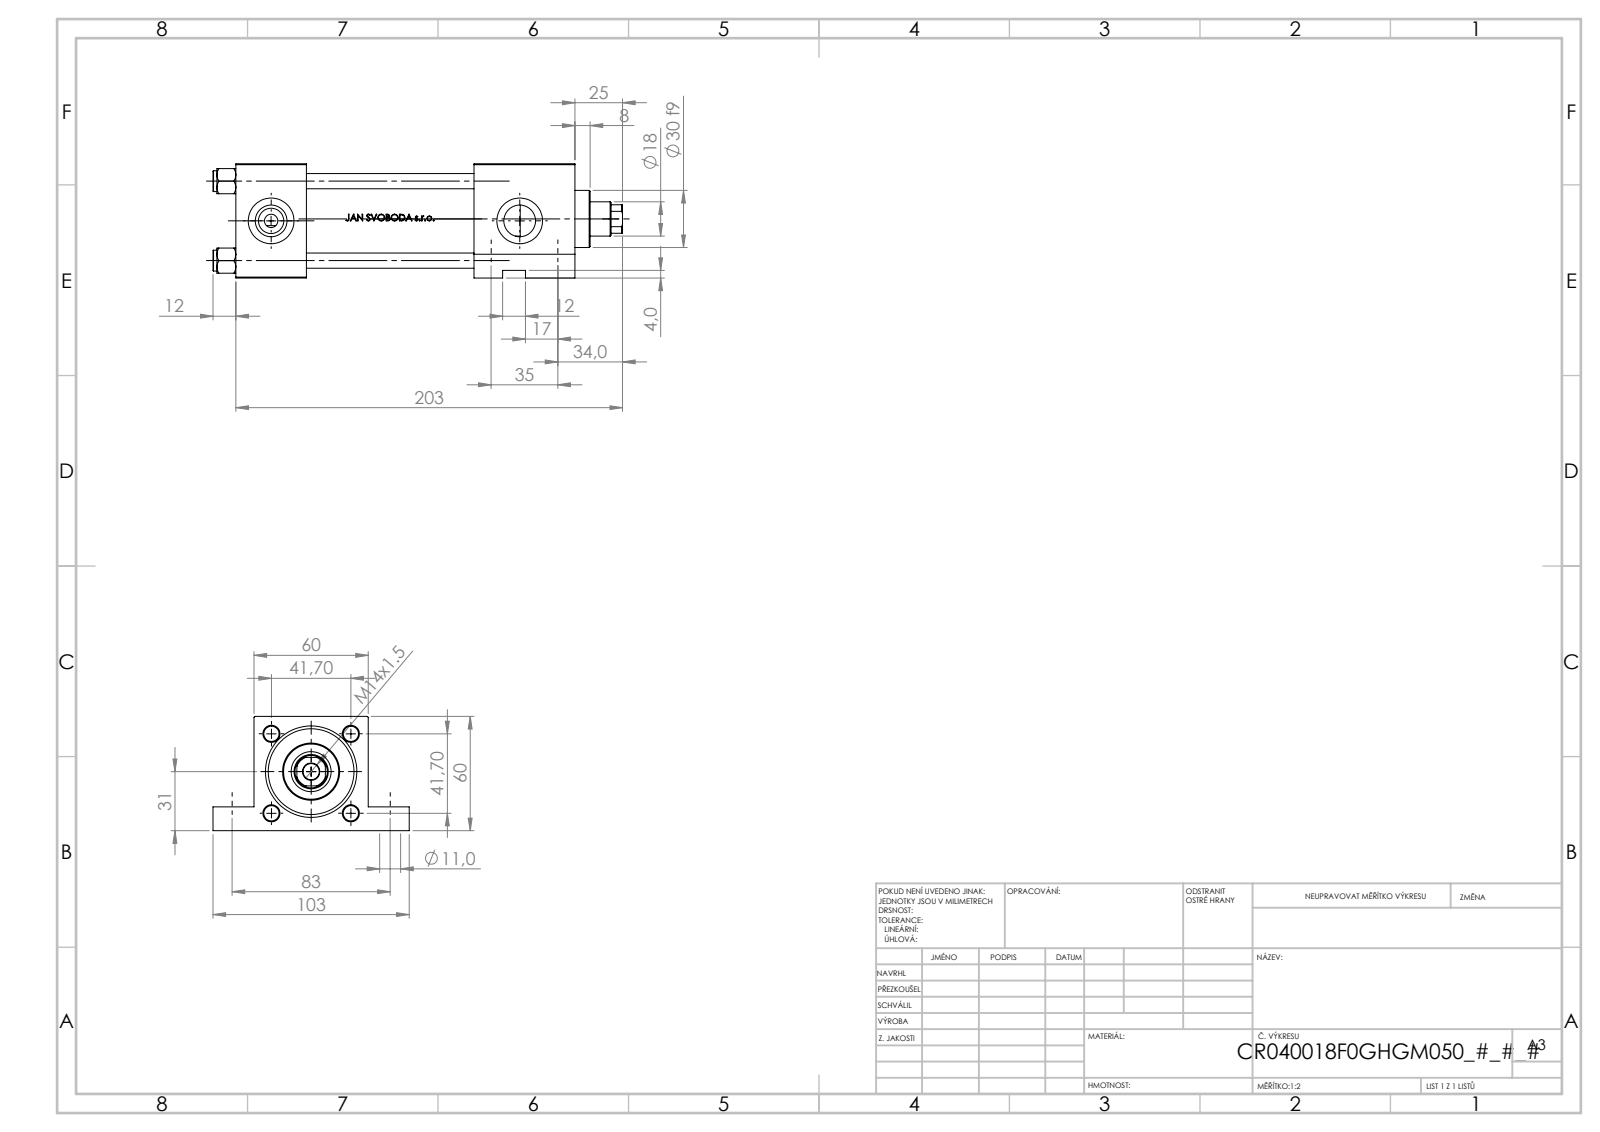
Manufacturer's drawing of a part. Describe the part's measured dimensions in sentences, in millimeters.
The part is named "NUT_M5_F; V215CR_VCP_F; V215CR_F_Body; V215CR_F_TYCINKA (+1 more)". Its 3-D file was written by "SolidWorks 2019 (CONFIG_CONTROL_DESIGN)". It is 11 solids with 1118 faces: 437 planar, 141 cylindrical and 540 other. Overall it measures 215 by 103 by 60 millimeters. Its volume is 449 455 cubic millimeters and its surface area 124 354 square millimeters. Round holes: 4 of diameter 8, 4 of diameter 11, 2 of diameter 7, 2 of diameter 16.66, 2 of diameter 24, 1 of diameter 8.5, 1 of diameter 18, 1 of diameter 21, 1 of diameter 31, 1 of diameter 40, 1 of diameter 45. Round bosses or shafts: 4 of diameter 11, 1 of diameter 46, 1 of diameter 30. Partial cylindrical surfaces (rounded edges, fillets, slot ends): 1 of radius 8.5. The main face-to-face distances are 60, 37, 178, 141, 125, 88, 53, 103, 149.3, 112.3. The hole center spacings are 41.7, 28.79, 30.2, 35, 58.97, 83, 90.08, 130.5.
